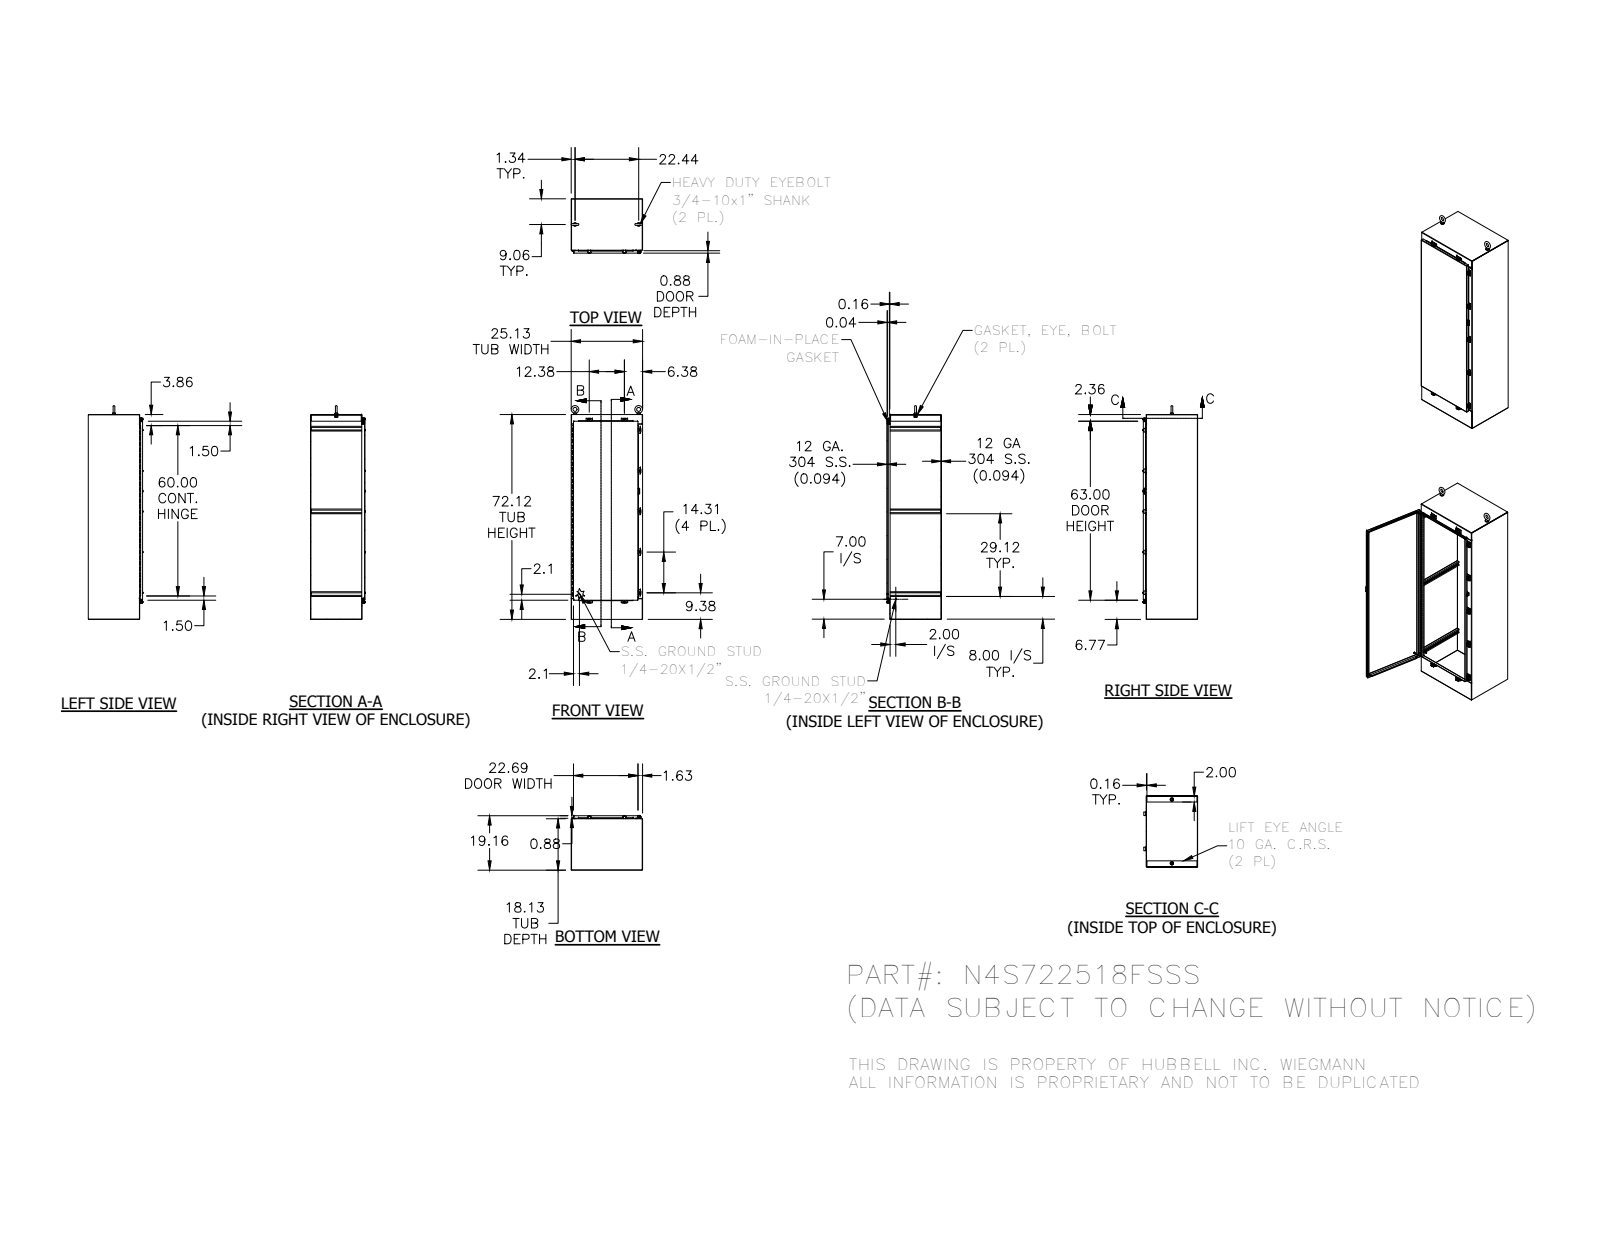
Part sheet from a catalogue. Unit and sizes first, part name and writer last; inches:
Units: inches
Overall size (bounding box): 75.248 × 25.125 × 19.355
Round holes (diameter × count): ⌀0.211 ×9, ⌀0.281 ×9, ⌀0.3 ×9, ⌀0.11 ×3, ⌀0.642 ×2, ⌀0.813 ×2, ⌀0.125 ×1, ⌀0.156 ×1, ⌀0.5 ×1
Round bosses / shafts (diameter × count): ⌀0.25 ×12, ⌀0.52 ×9, ⌀0.5 ×9, ⌀0.35 ×9, ⌀1.25 ×2, ⌀1.12 ×2, ⌀0.75 ×2, ⌀0.337 ×2
Partial cylindrical surfaces — rounded edges, fillets, slot ends (radius × count): R0.03 ×107, R0.125 ×43, R0.062 ×22, R0.25 ×21, R0.031 ×19, R0.019 ×18, R0.053 ×18, R0.086 ×18
Main face-to-face distances: 0.094, 19.067, 25.031, 18.973, 19.161, 24.938, 25.125, 18.031, 1.035, 72.031
Hole centre spacings: 14.313, 28.626, 0.789, 12.38, 42.939, 64.375, 65.554, 0.449
Volume: 861.7 in³ · Surface area: 17 693 in²
Bodies: 78 solids, 3000 faces (1210 planar, 1210 cylindrical, 580 other)
Part name (STEP PRODUCT): HSSN1300W60L_1; 349132_1; N4S25.13FSSSDS_1; N4S7225FSSSFIP_1 (+8 more)
STEP written by: SolidWorks 2014 (AUTOMOTIVE_DESIGN)
